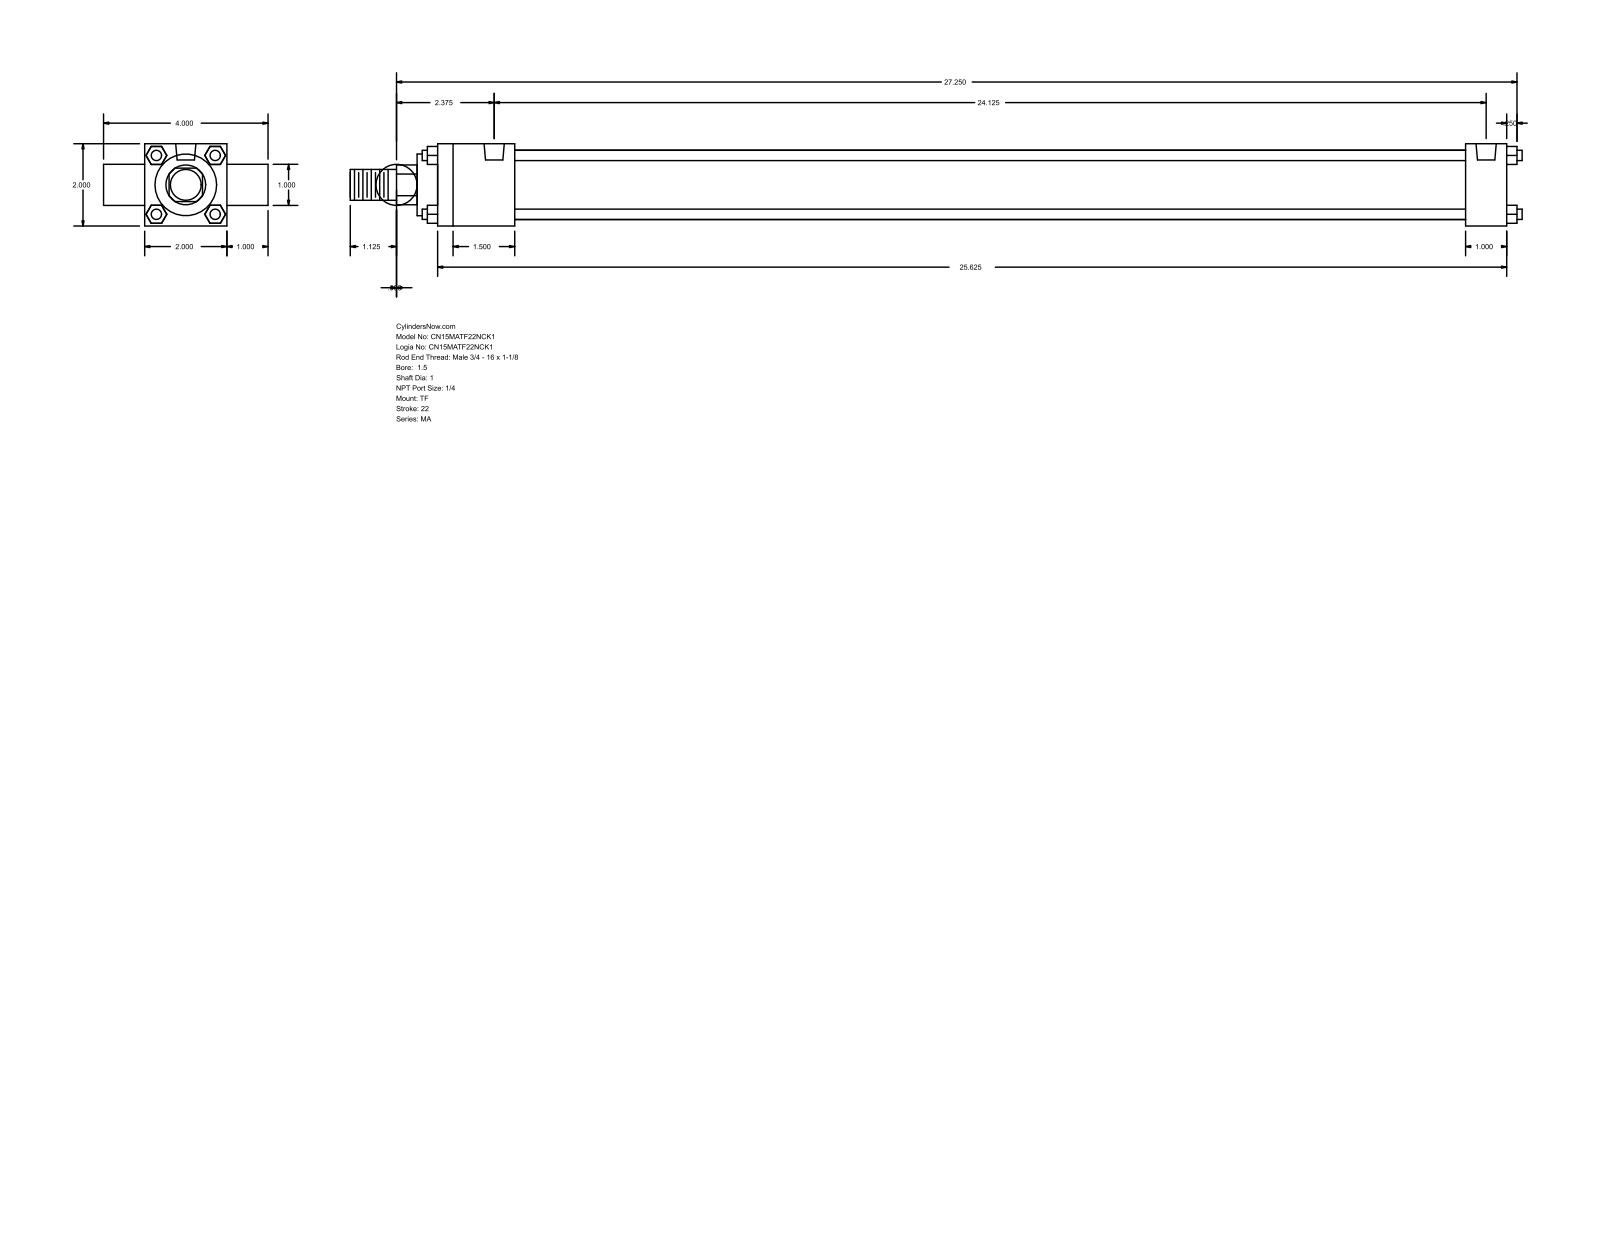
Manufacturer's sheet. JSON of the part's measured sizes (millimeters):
{"part_name": "MA_TF__0150_1", "step_written_by": "GSSL Pune (CONFIG_CONTROL_DESIGN)", "units": "millimeters", "bodies": {"solids": 0, "faces": 120, "planar": 92, "cylindrical": 28, "other": 0}, "overall_size": [723.9, 101.6, 50.8], "round_holes": [[7.94, 3], [12.49, 2]], "round_bosses_or_shafts": [[6.35, 4], [25.4, 2], [42.93, 1], [38.1, 1], [19.05, 1]], "partial_cylinders_radius": [[12.29, 1]], "face_to_face_distances": [50.8, 25.4, 660.4, 76.2, 6.35, 47.63, 635, 587.37, 612.77, 673.1], "hole_center_spacings": [612.77]}
